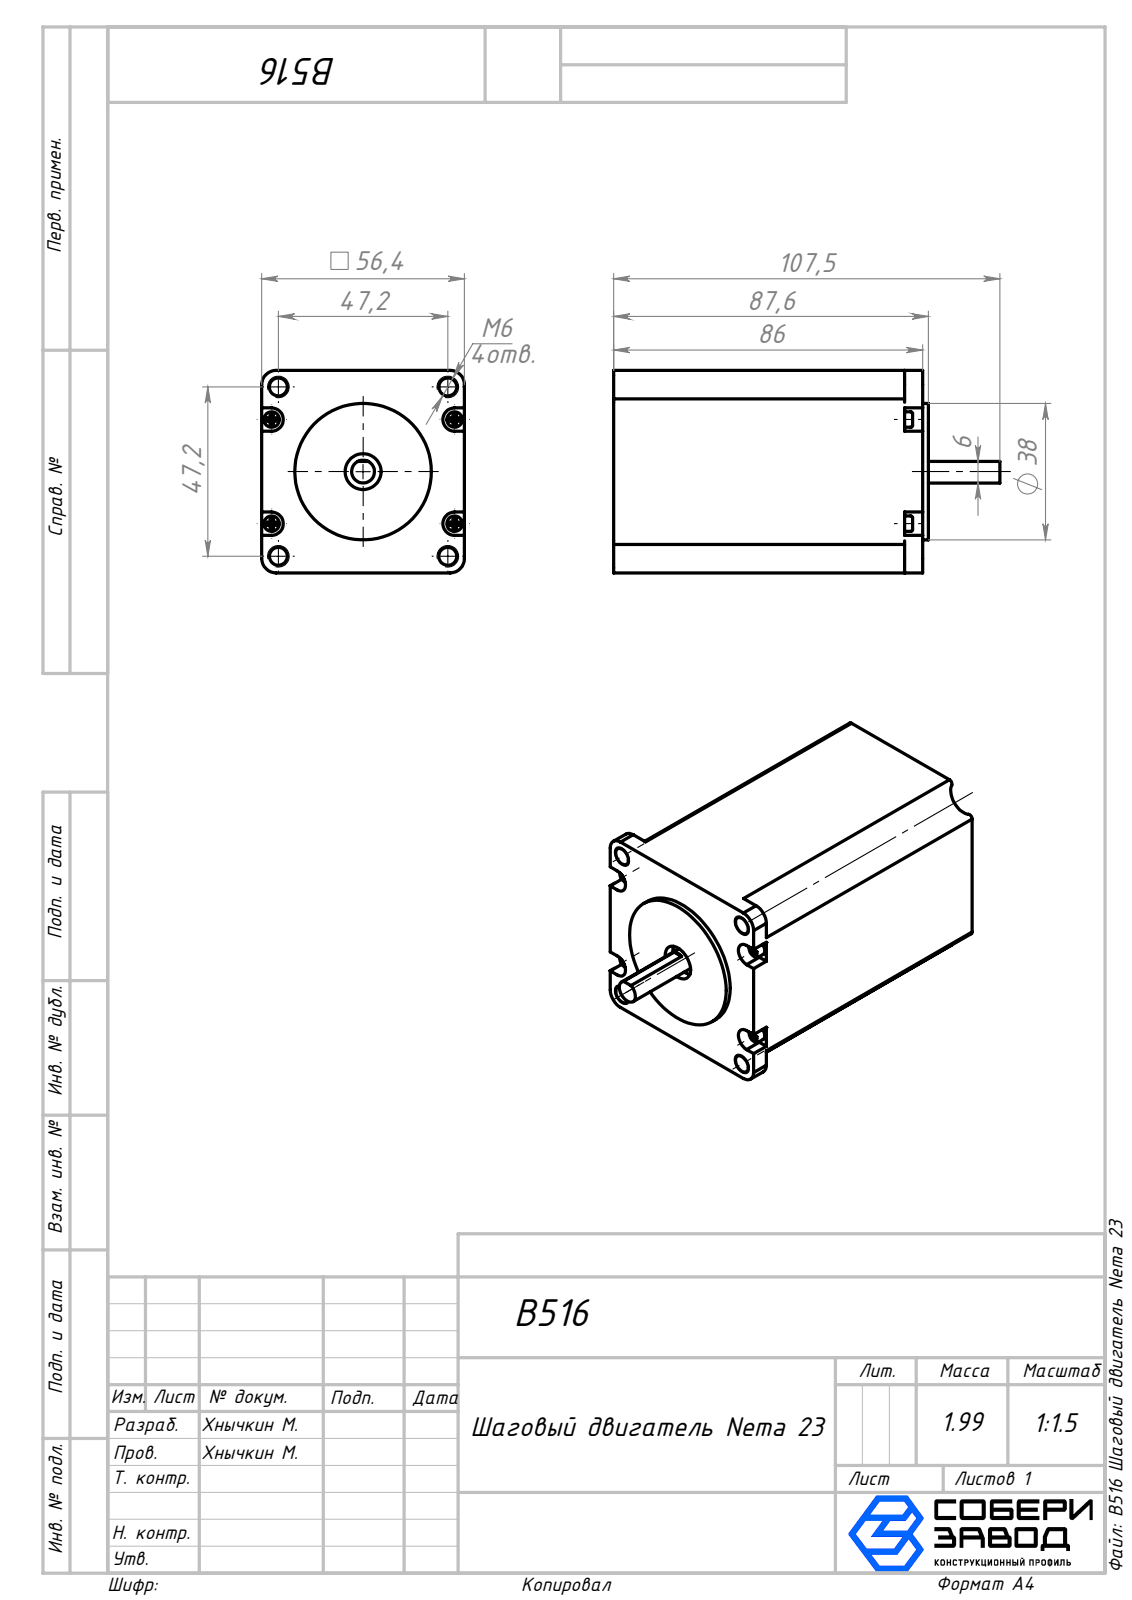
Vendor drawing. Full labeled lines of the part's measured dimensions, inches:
Part name (STEP PRODUCT): B516 Шаговый двигатель Nema 23
STEP written by: SolidWorks 2026 (AUTOMOTIVE_DESIGN)
Units: inches
Bodies: 1 solid, 142 faces (84 planar, 50 cylindrical, 8 other)
Overall size (bounding box): 4.232 × 2.22 × 2.22
Volume: 15.48 in³ · Surface area: 41.06 in²
Round holes (diameter × count): ⌀0.197 ×4, ⌀0.394 ×1
Round bosses / shafts (diameter × count): ⌀0.169 ×4, ⌀1.496 ×1, ⌀0.25 ×1
Partial cylindrical surfaces — rounded edges, fillets, slot ends (radius × count): R0.039 ×8, R0.128 ×4, R0.157 ×4, R0.197 ×4
Main face-to-face distances: 2.22, 3.386, 3.449, 0.063, 3.189, 0.197, 0.26, 0.157, 3.031, 3.228
Hole centre spacings: 1.856, 1.312, 1.313, 2.625, 1.857
